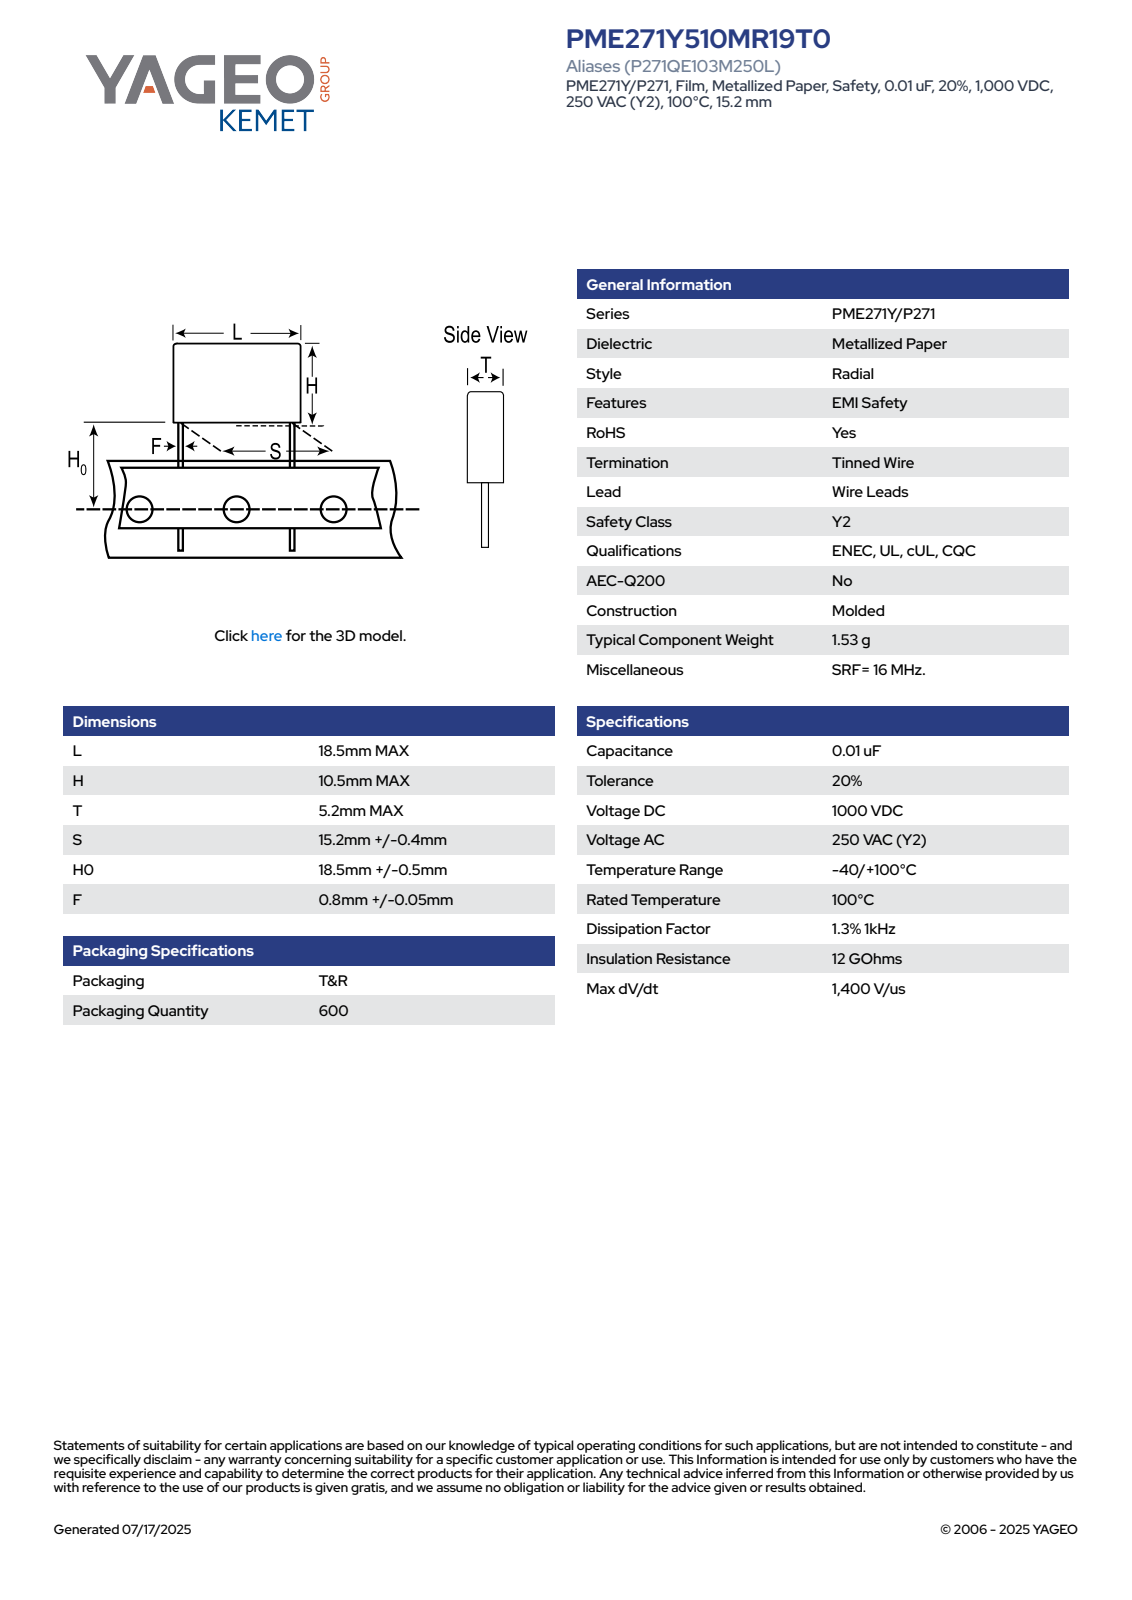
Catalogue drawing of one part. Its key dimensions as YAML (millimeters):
part_name: "CFR_MOLDED_18.5X10.5X5.2_L18.5H10.5T5.2S15.2H019F0.85"
step_written_by: "SolidWorks 2014 (AUTOMOTIVE_DESIGN)"
units: millimeters
bodies: {solids: 4, faces: 73, planar: 65, cylindrical: 8, other: 0}
overall_size: [29.5, 18.5, 5.21]
volume: 1029
surface_area: 798
round_bosses_or_shafts:
  - {diameter: 0.85, count: 2}
partial_cylinders:
  - {radius: 0.5, count: 4}
face_to_face_distances: [5.2, 10.5, 18.5, 19, 29.5, 25.06, 6.06, 4.44, 23.4, 4.4]
